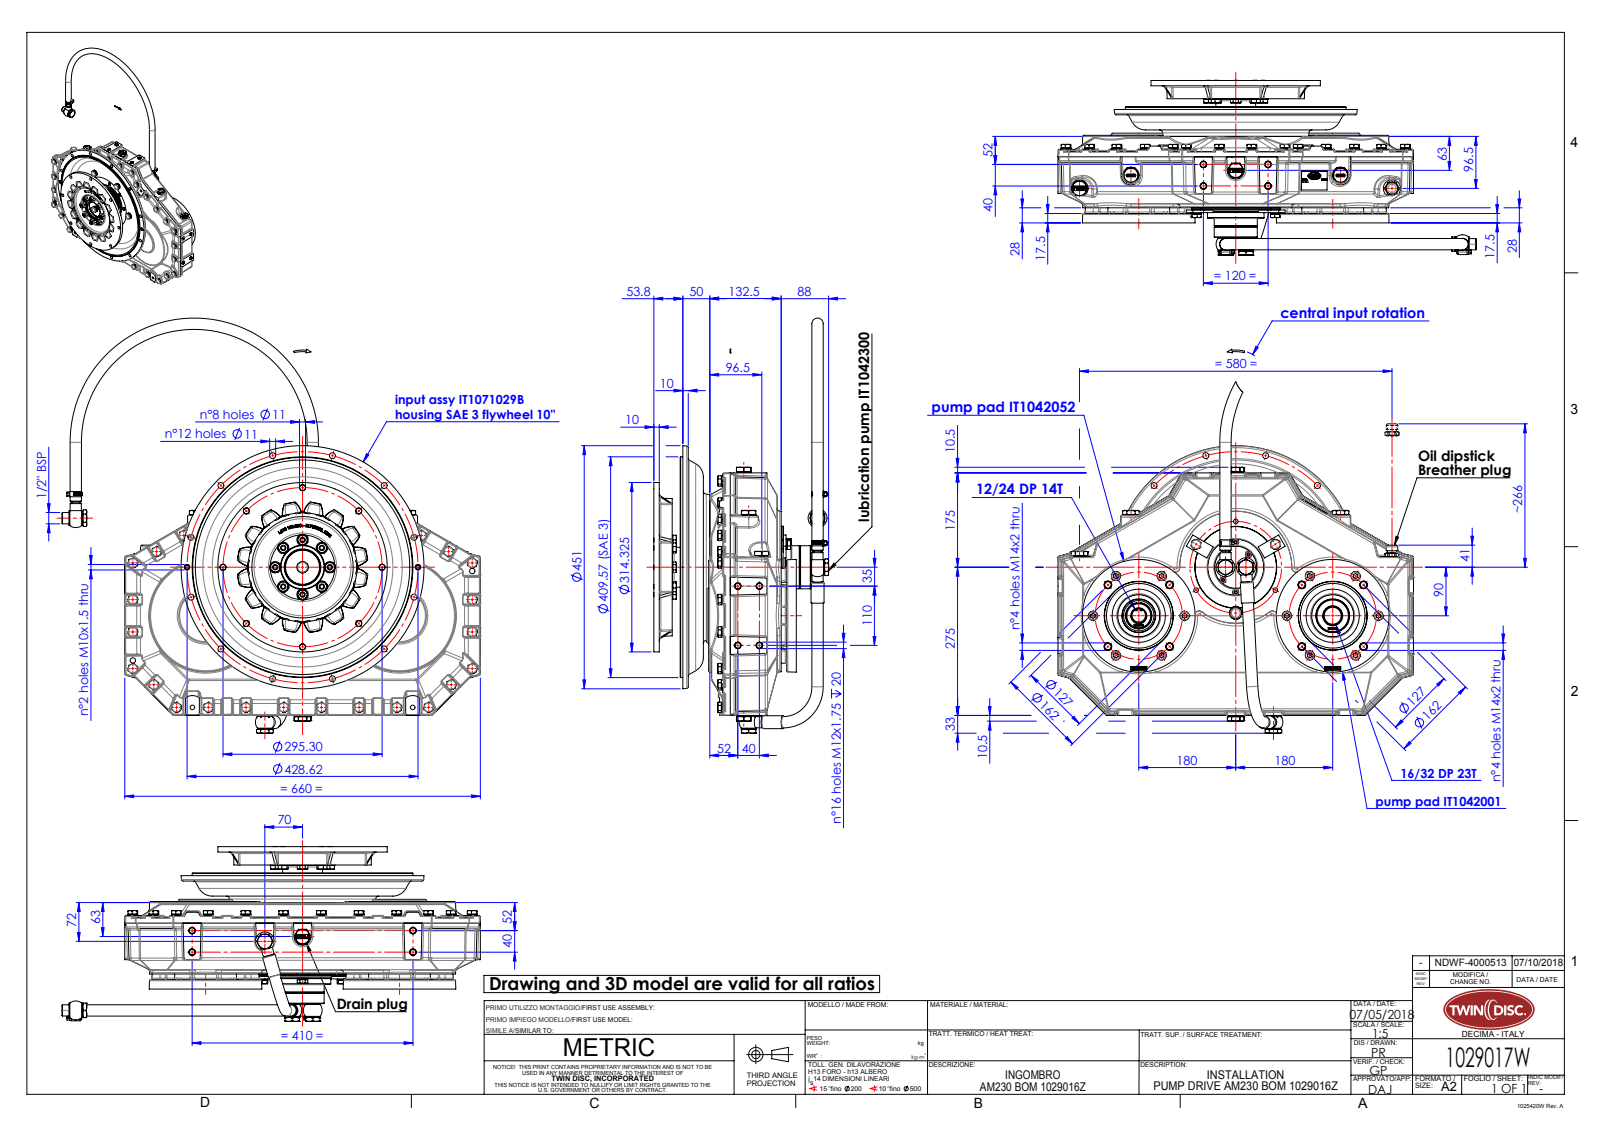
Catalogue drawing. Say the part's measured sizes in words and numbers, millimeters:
The part is named "1029017W; IT1071029B-installation; IT1042300_A-installation; IT1042001_rev00-installation (+6 more)". Its 3-D file was written by "SolidWorks 2015 (AUTOMOTIVE_DESIGN)". It is 82 solids with 9376 faces: 4252 planar, 2289 cylindrical and 2835 other. Overall it measures 776.5 by 770.2 by 324.5 millimeters. Its volume is 6 888 000 cubic millimeters and its surface area 3 395 000 square millimeters. Round holes: 48 of diameter 10.5, 41 of diameter 10.2, 33 of diameter 11, 32 of diameter 8.5, 20 of diameter 12, 15 of diameter 13, 12 of diameter 17, 10 of diameter 8, 10 of diameter 10, 10 of diameter 21, 8 of diameter 10.7, 8 of diameter 14. Round bosses or shafts: 61 of diameter 10, 41 of diameter 16.2, 32 of diameter 18.1, 12 of diameter 16, 11 of diameter 18, 10 of diameter 21, 7 of diameter 21.1, 7 of diameter 12. Partial cylindrical surfaces (rounded edges, fillets, slot ends): 217 of radius 2, 159 of radius 3, 110 of radius 2.5, 90 of radius 5, 68 of radius 1, 64 of radius 4, 58 of radius 0.45, 32 of radius 42.91. The main face-to-face distances are 40, 38, 10, 28, 20, 21, 94.5, 132.5, 48, 19. The hole center spacings are 120, 57.4, 75, 138.58, 40, 207.84, 22.59, 51.37.
